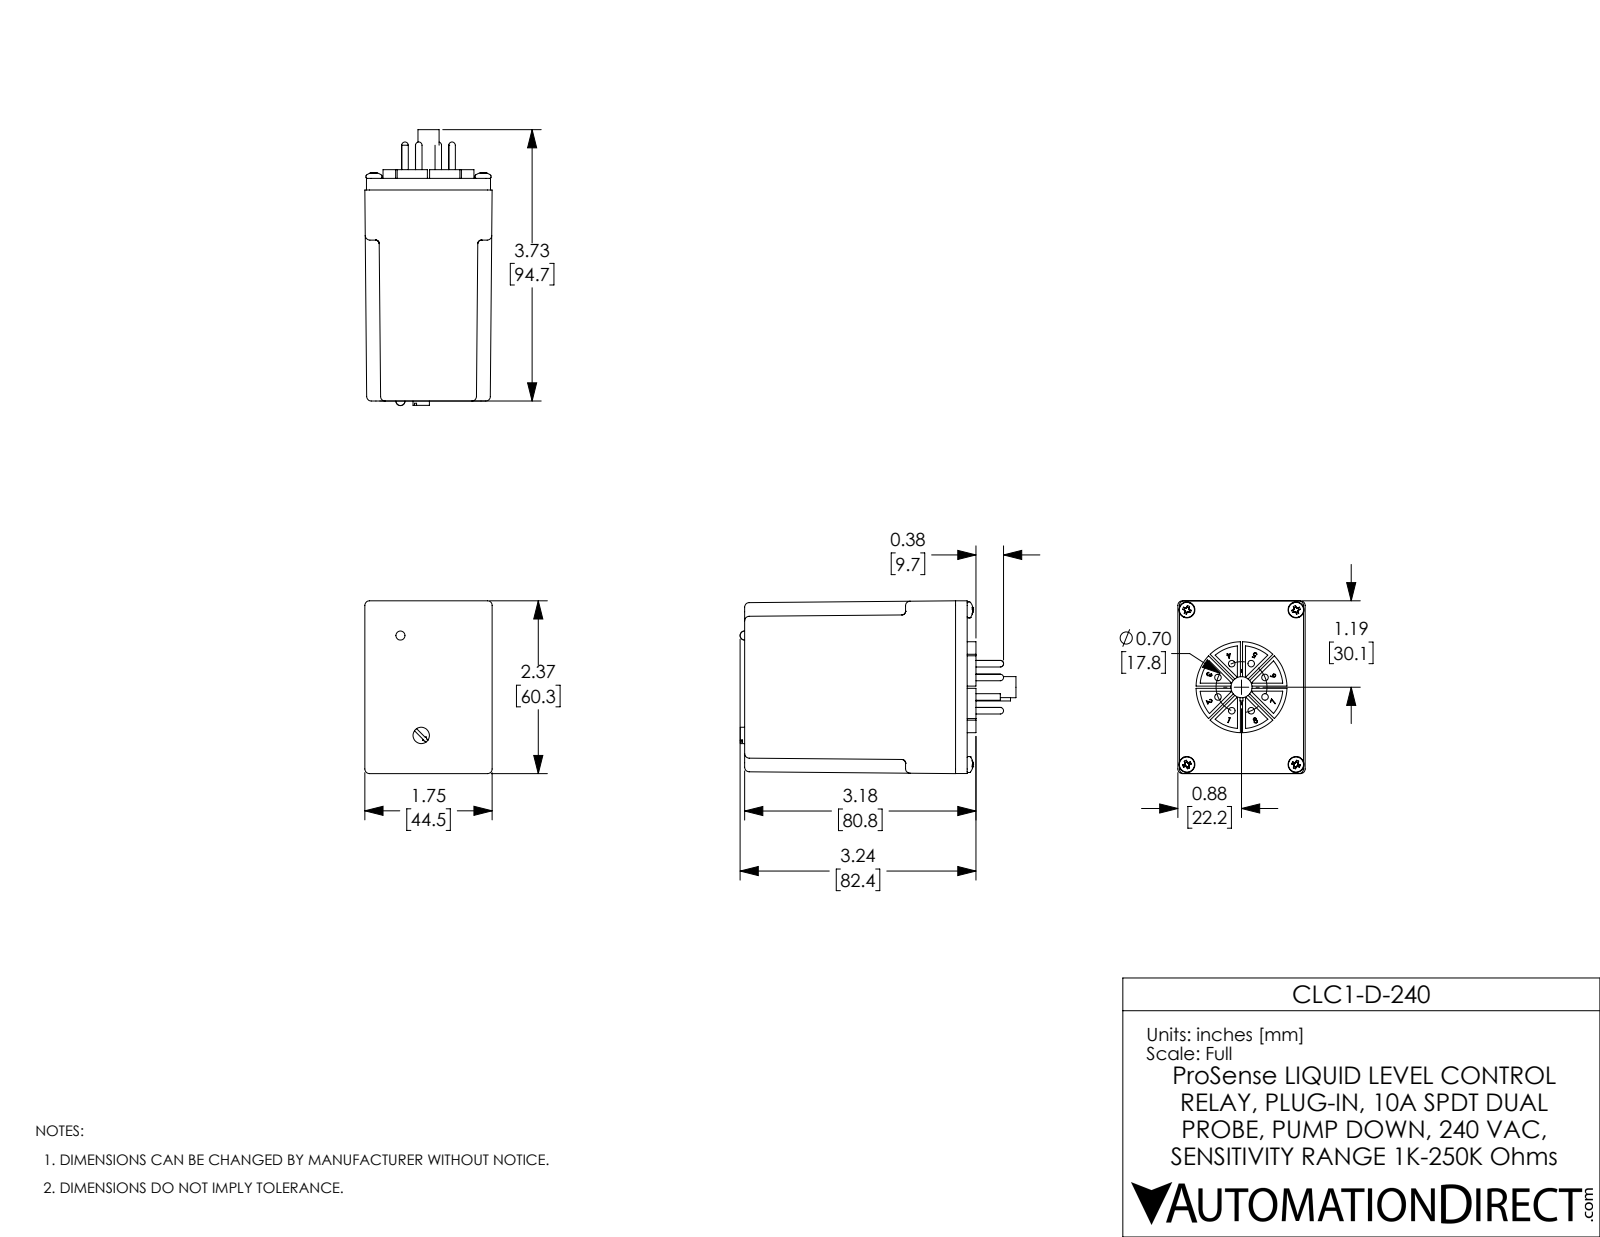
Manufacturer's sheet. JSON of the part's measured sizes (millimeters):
{"part_name": "CLC1-D-240", "step_written_by": "SolidWorks 2017 (AUTOMOTIVE_DESIGN)", "units": "millimeters", "bodies": {"solids": 16, "faces": 706, "planar": 229, "cylindrical": 294, "other": 183}, "overall_size": [96.3, 60.3, 44.5], "volume_mm3": 200600, "surface_area_mm2": 28850, "round_holes": [[3.2, 4]], "round_bosses_or_shafts": [[2.3, 8], [5.6, 4], [2.8, 4], [2, 4], [31.8, 1], [7.4, 1], [5.7, 1]], "partial_cylinders_radius": [[1.6, 32], [0.1, 8], [1.3, 4], [14.5, 1]], "face_to_face_distances": [73.7, 4.1, 77.7, 1.8, 5.8, 79.5, 4.8, 0.8, 80.8, 1.3], "hole_center_spacings": [38.1, 54, 66.1]}
